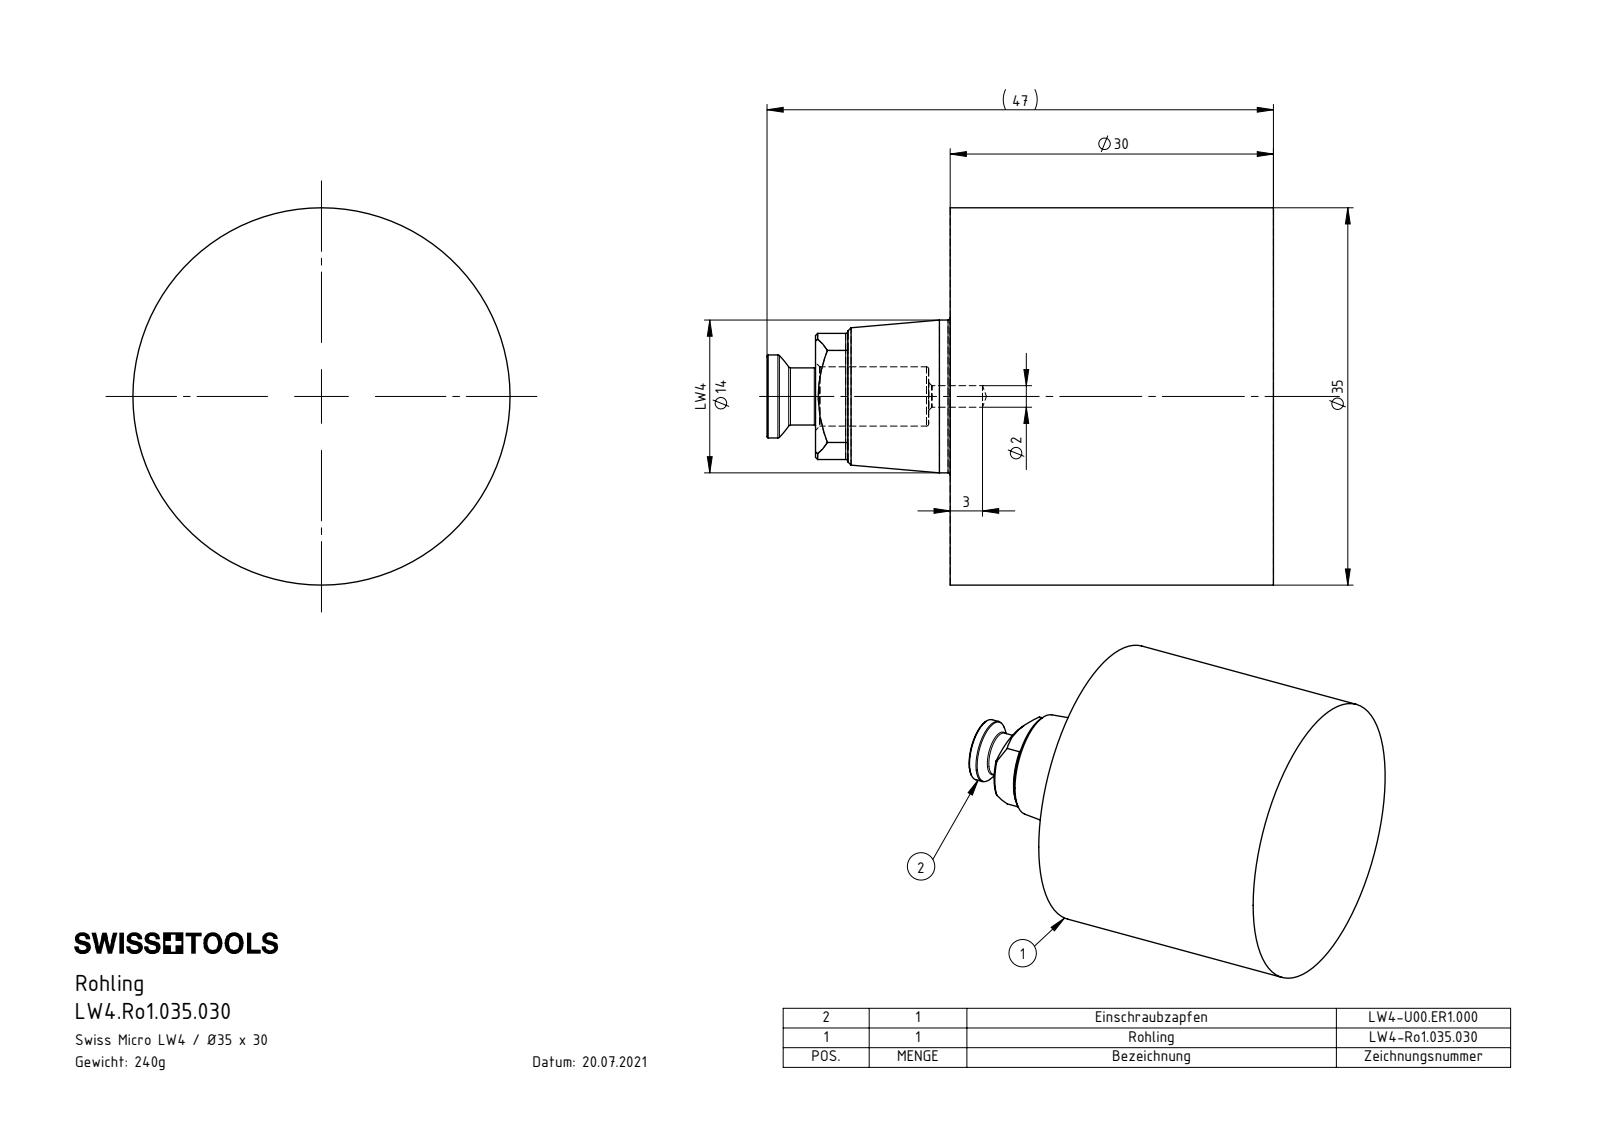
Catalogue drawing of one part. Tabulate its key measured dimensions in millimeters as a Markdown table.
| quantity | value |
| --- | --- |
| part name | LW4.Ro1.035.030; LW4-Ro1.035.030_A; LW4-U00.ER1.000_B |
| STEP written by | SolidWorks 2017 (AUTOMOTIVE_DESIGN) |
| units | millimeters |
| bodies | 2 solids, 53 faces (15 planar, 13 cylindrical, 25 other) |
| overall size | 47 × 35 × 35 |
| volume | 30 553 mm³ |
| surface area | 6 344 mm² |
| round holes (diameter × count) | 2 × 1, 2.5 × 1, 5.5 × 1 |
| round bosses / shafts (diameter × count) | 35 × 1, 14.17 × 1, 7.7 × 1, 6 × 1, 5.3 × 1, 5 × 1 |
| partial cylindrical surfaces (radius × count) | 0.2 × 2, 5.85 × 1 |
| main face-to-face distances | 30, 7.5, 2, 12.5, 42.5, 4.5, 17, 47, 15, 10.5 |
